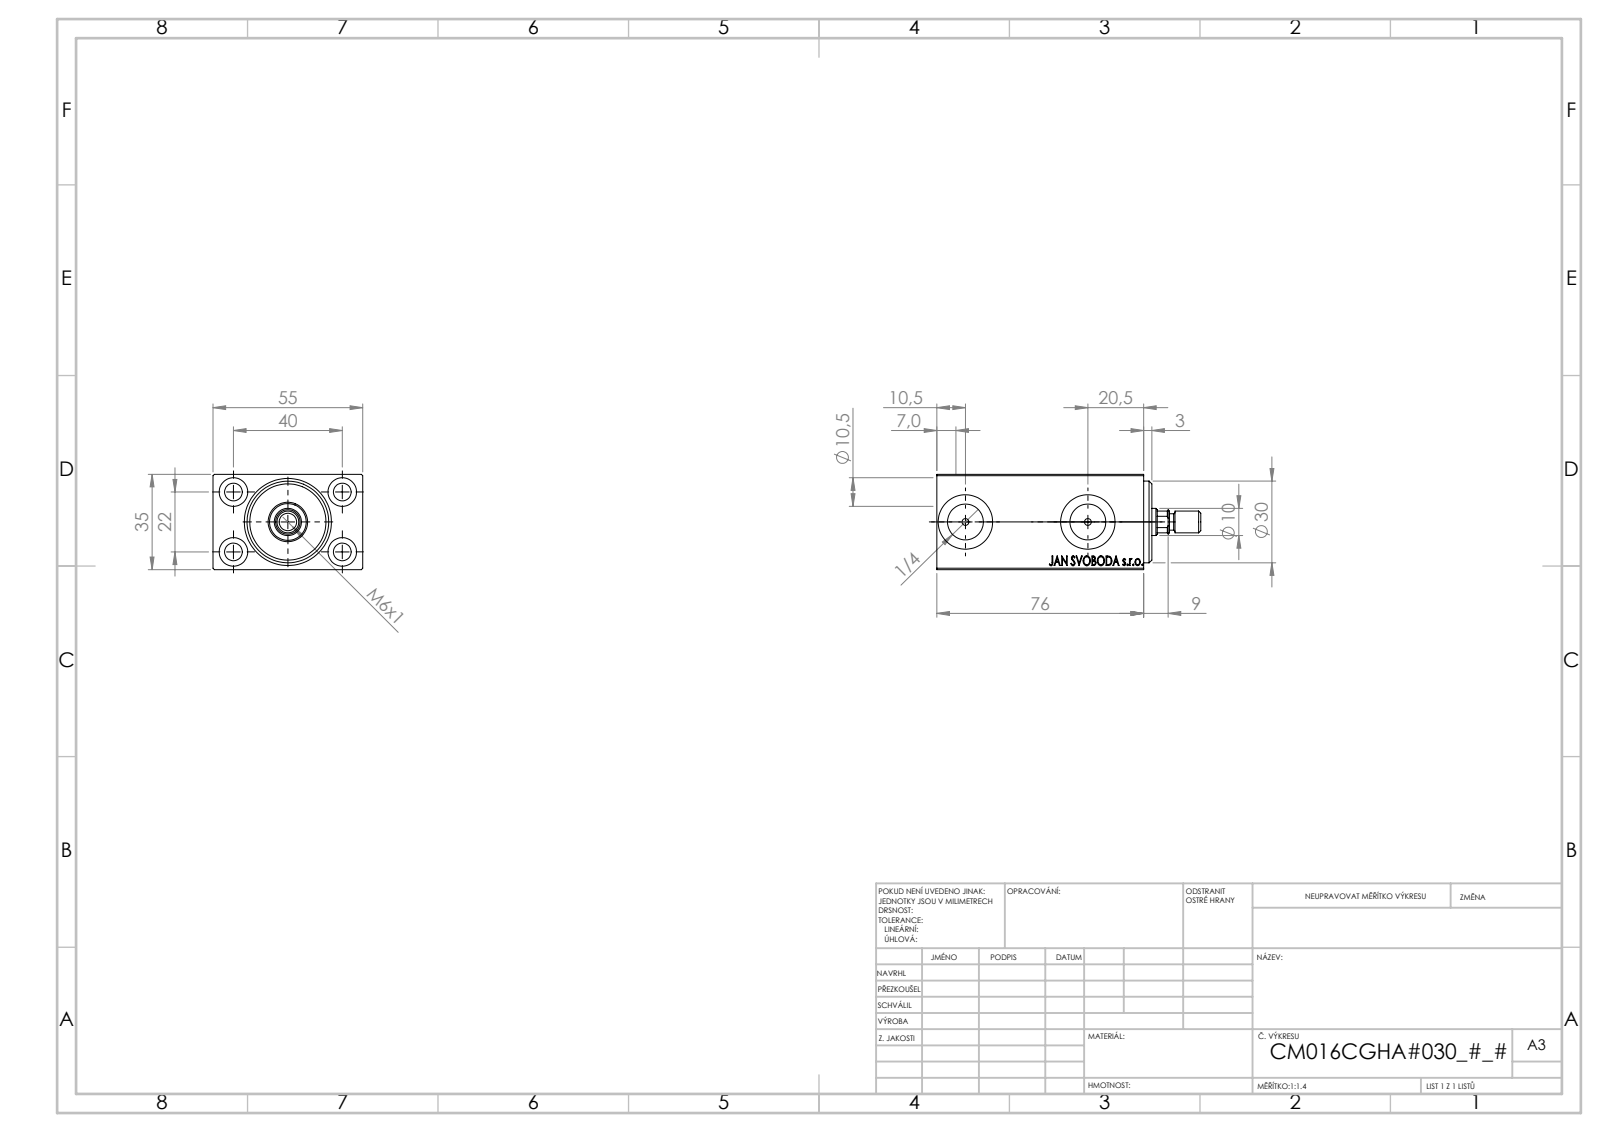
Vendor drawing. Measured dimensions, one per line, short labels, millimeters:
name: V450CM_C_Body; V450CM_C_VCP; V450CM_MALE_METRIC; V450CM_VC_B
written by: SolidWorks 2019 (CONFIG_CONTROL_DESIGN)
unit: mm
bodies: 4 solids, 879 faces (413 planar, 66 cylindrical, 400 other)
size: 97 × 55 × 35
volume: 128 526 mm³; area: 35 819 mm²
holes: 4× ⌀6.5, 4× ⌀10.5, 2× ⌀2.5, 2× ⌀13.16, 2× ⌀20, 1× ⌀4.5, 1× ⌀10, 1× ⌀13.5, 1× ⌀14.5, 1× ⌀16, 1× ⌀18, 1× ⌀30
bosses: 1× ⌀8, 1× ⌀6
rounds: 1× R4.5
face distances: 35, 55, 71, 5, 76, 2, 8, 3, 79, 7
hole spacings: 22.83, 22, 40, 45.65, 45
